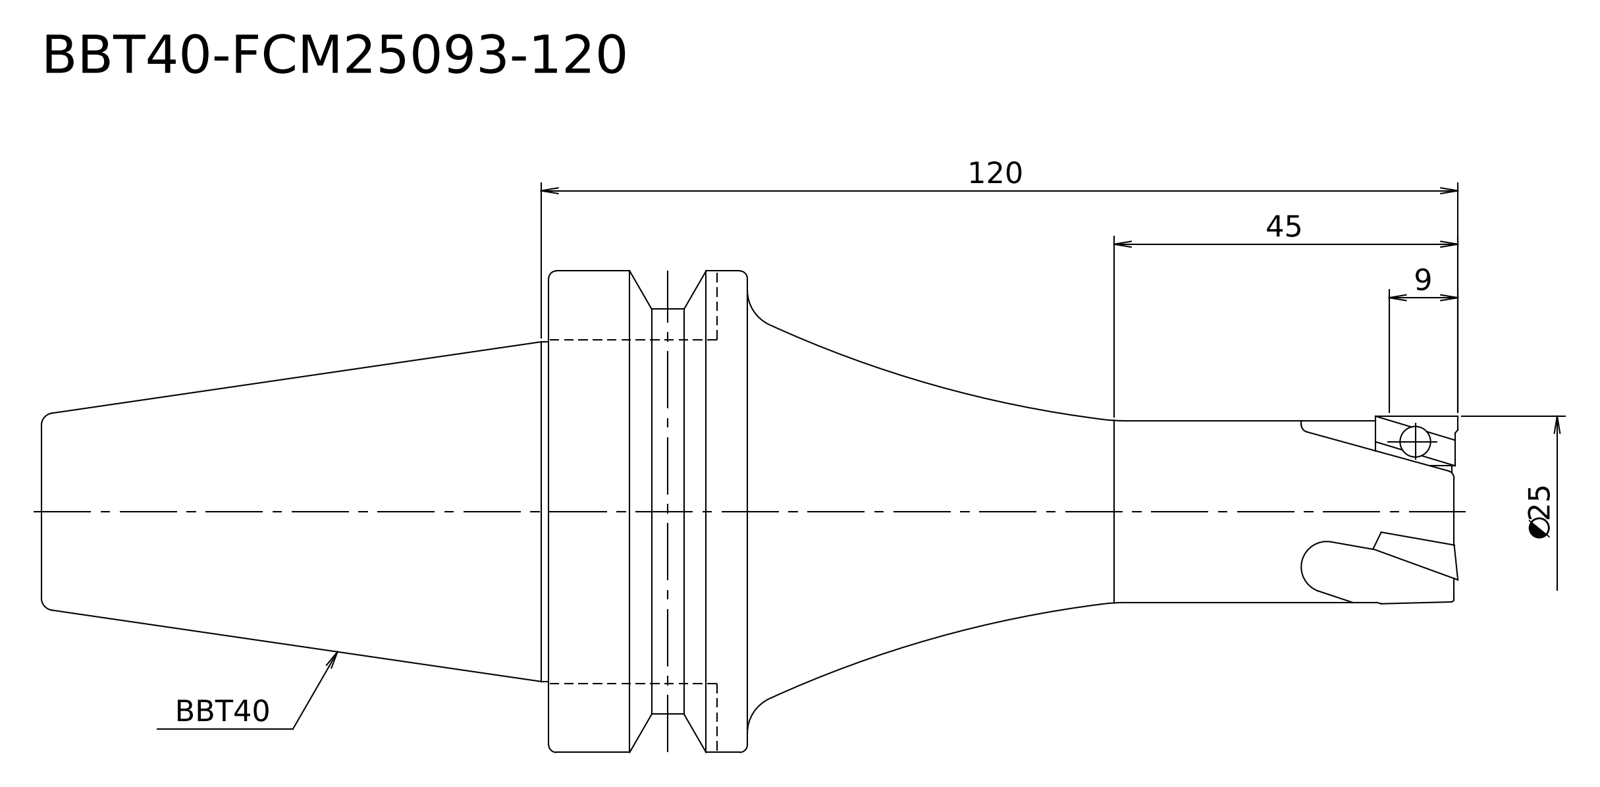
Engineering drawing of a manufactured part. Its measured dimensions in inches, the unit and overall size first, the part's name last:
Units: inches
Overall size (bounding box): 7.299 × 2.48 × 2.48
Round bosses / shafts (diameter × count): ⌀2.48 ×1, ⌀2.087 ×1, ⌀1.75 ×1, ⌀0.984 ×1, ⌀0.937 ×1
Main face-to-face distances: 2.614, 4.685, 7.299, 3.661, 1.024, 3.638
Volume: 13.15 in³ · Surface area: 40.36 in²
Bodies: 1 solid, 17 faces (4 planar, 6 cylindrical, 7 other)
STEP written by: Kubotek KeyCreator V8.5.1 (14335) (CONFIG_CONTROL_DESIGN)
